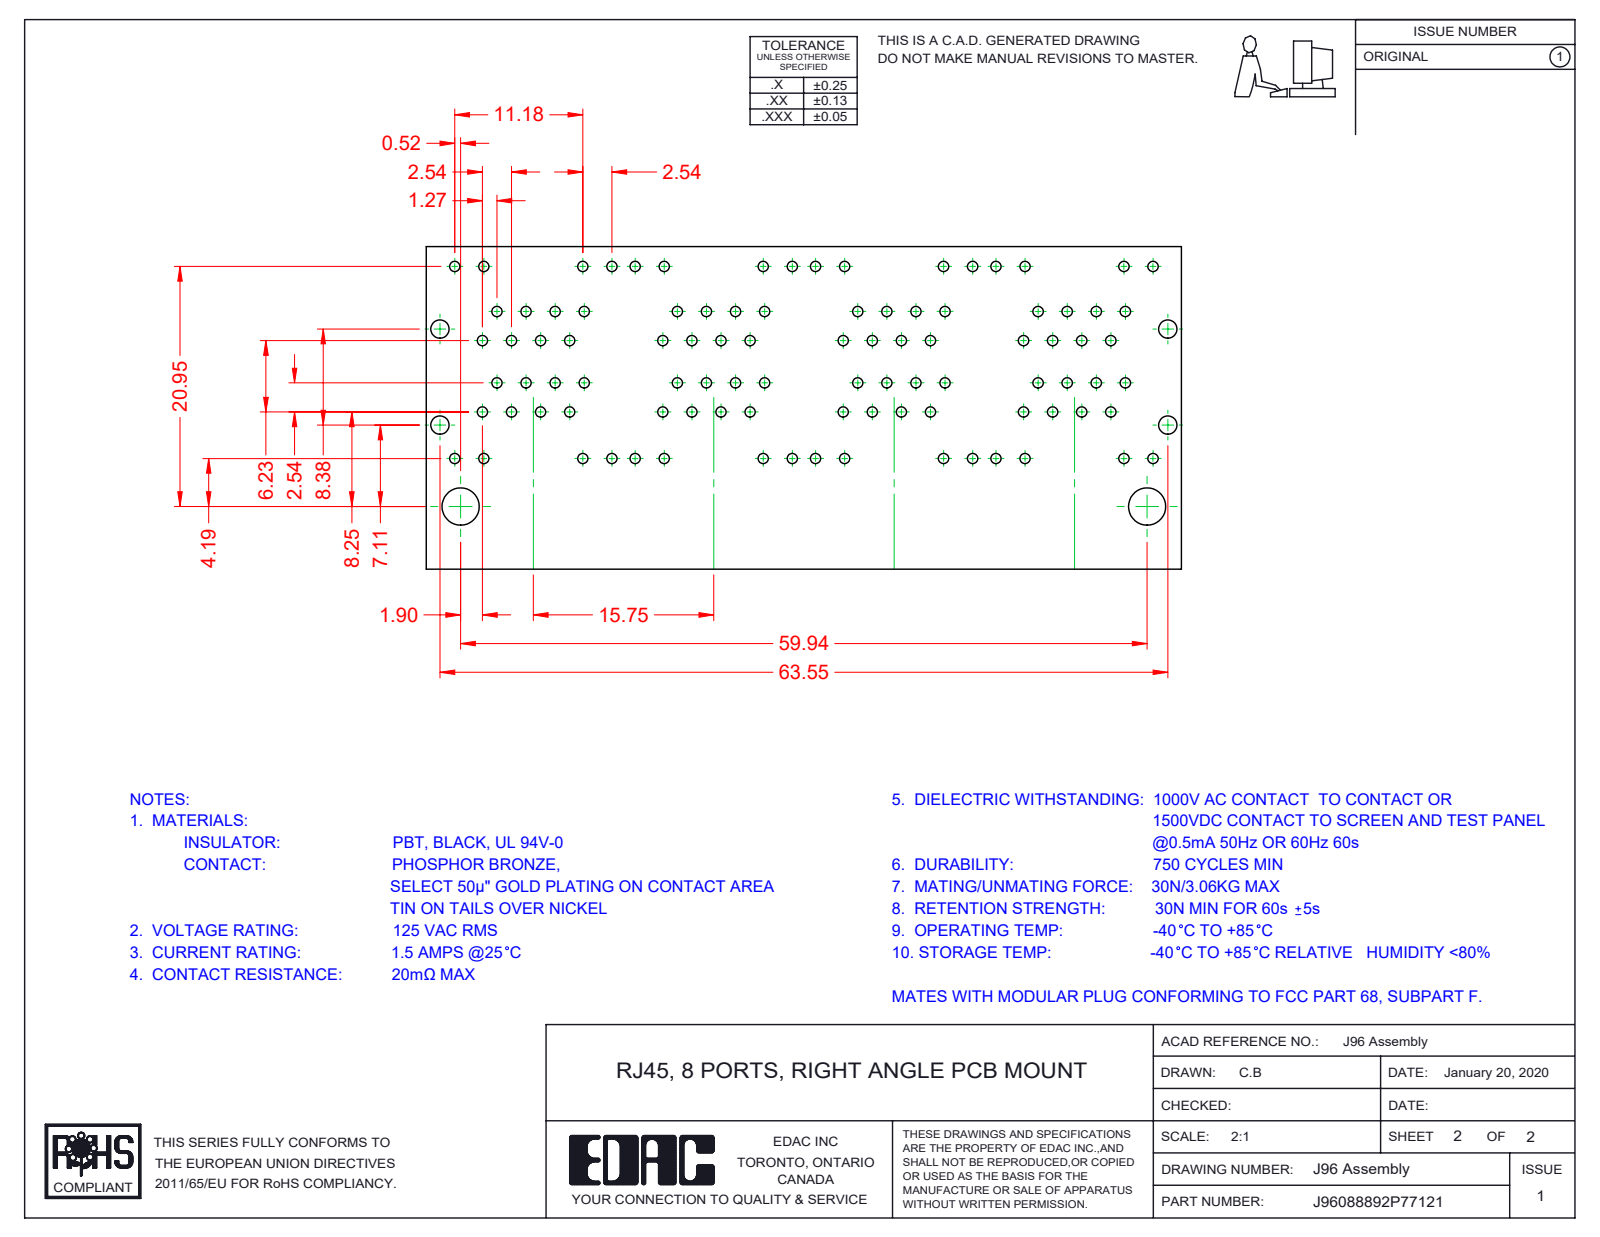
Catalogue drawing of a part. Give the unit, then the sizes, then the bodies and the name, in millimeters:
Units: millimetres
Overall size (bounding box): 64.05 × 29.58 × 28.68
Round holes (diameter × count): ⌀1.7 ×3
Round bosses / shafts (diameter × count): ⌀1.68 ×3
Partial cylindrical surfaces — rounded edges, fillets, slot ends (radius × count): R0.25 ×124, R0.35 ×73, R1 ×72, R0.5 ×49, R0.91 ×32, R0.2 ×21, R0.7 ×11, R0.22 ×8
Main face-to-face distances: 15.75, 0.35, 9.95, 1.17, 1.6, 0.54, 9.98, 10.18, 12.67, 3.37
Hole centre spacings: 15.75, 31.5
Volume: 24 160 mm³ · Surface area: 63 658 mm²
Bodies: 96 solids, 7674 faces (6069 planar, 1339 cylindrical, 266 other)
Part name (STEP PRODUCT): 96 LED RH Upper_7-Green-Orange; 96 LED RH Lower_7-Green-Orange; 96 Contact Lock Lower; 96 Insulator_8 Ports (+8 more)
STEP written by: SolidWorks 2016 (CONFIG_CONTROL_DESIGN)
